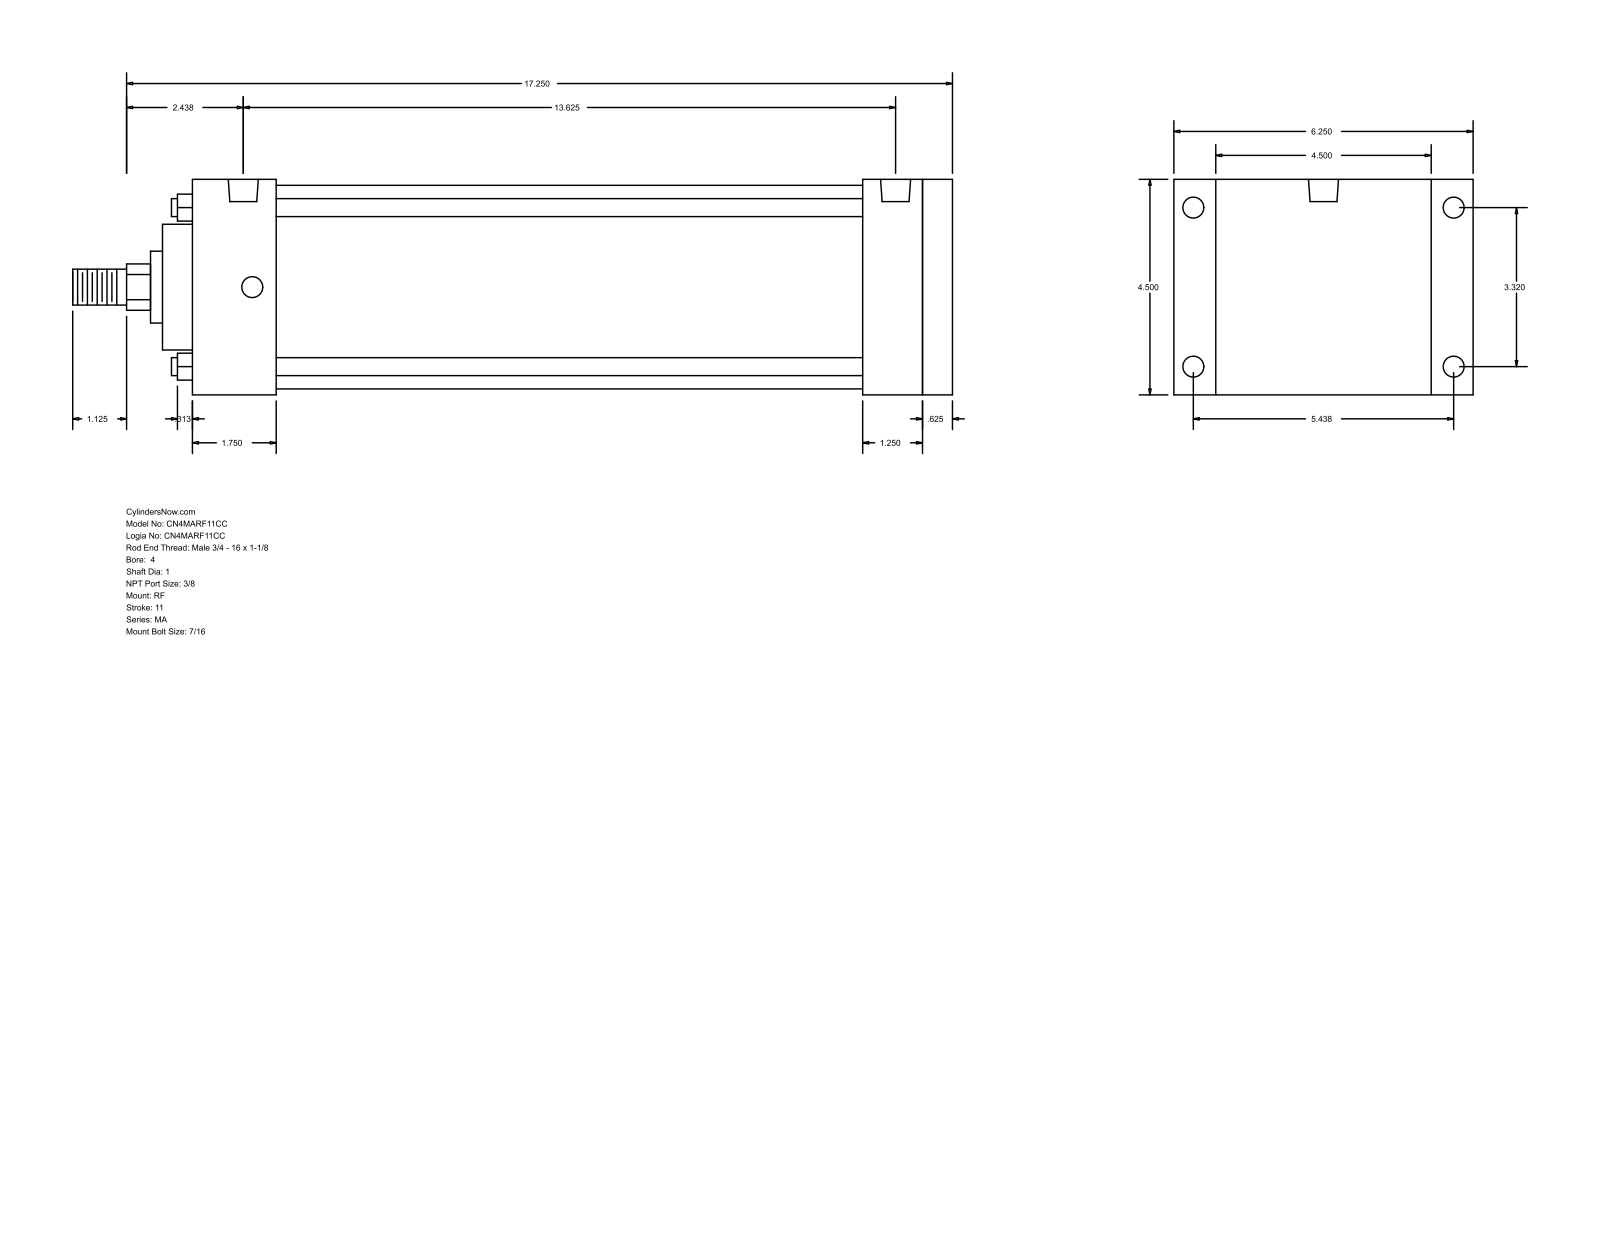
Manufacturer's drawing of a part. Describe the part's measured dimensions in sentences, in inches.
The part is named "MA_RF__0400_1". Its 3-D file was written by "GSSL Pune (CONFIG_CONTROL_DESIGN)". It is 0 solids with 94 faces: 65 planar, 29 cylindrical and 0 other. Overall it measures 18.375 by 6.25 by 4.5 inches. Round holes: 8 of diameter 0.437, 2 of diameter 0.627. Round bosses or shafts: 4 of diameter 0.375, 1 of diameter 4.25, 1 of diameter 2.625, 1 of diameter 1.5, 1 of diameter 1, 1 of diameter 0.75. Partial cylindrical surfaces (rounded edges, fillets, slot ends): 1 of radius 0.484. The main face-to-face distances are 4.5, 15.875, 15.25, 0.625, 0.875, 5.375, 14, 1.25, 1.875, 1.75. The hole center spacings are 0.187, 3.32, 5.438, 6.371, 13.25, 13.438, 13.625.
